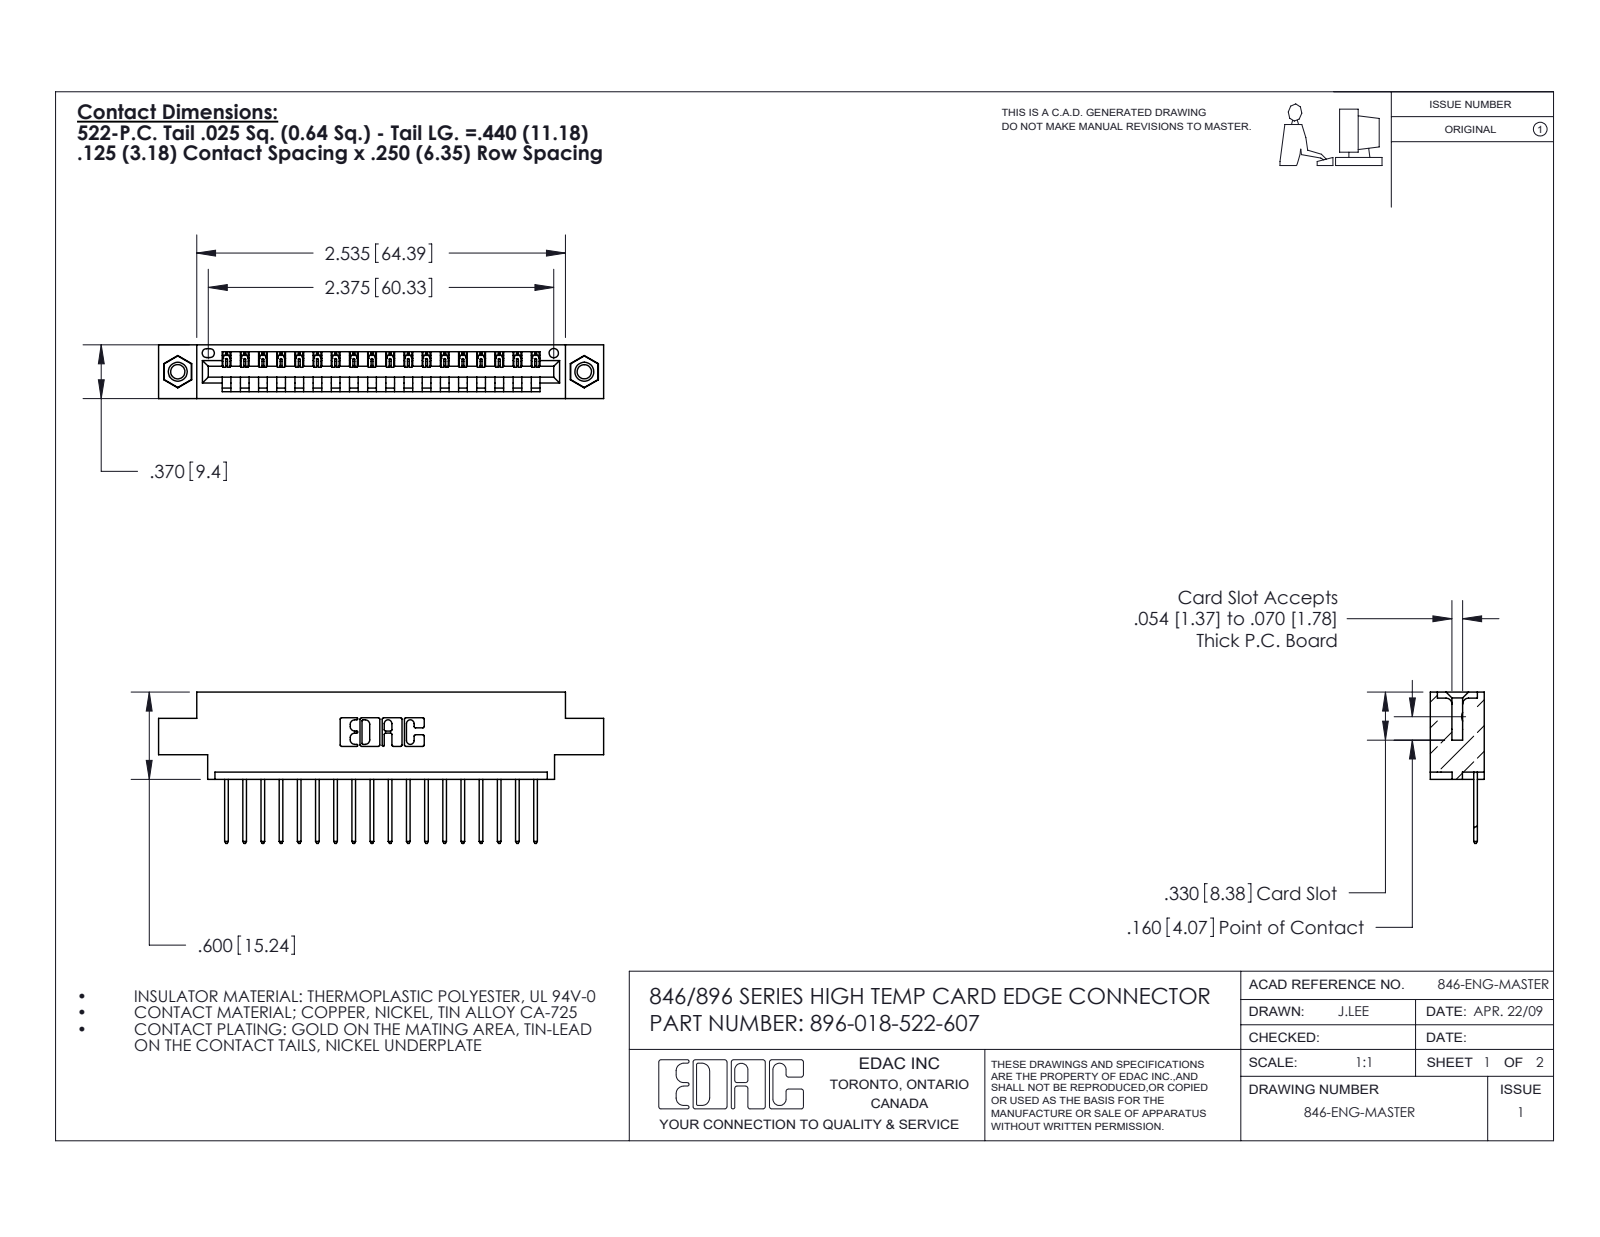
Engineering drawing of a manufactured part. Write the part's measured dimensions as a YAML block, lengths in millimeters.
part_name: "346 Part_0.170 Offset - 0.156 Dia-TI; 396-018-522-607; 345-250-001_345-250-005-103; 345-292-001_345-293-122"
step_written_by: "SolidWorks 2016 (CONFIG_CONTROL_DESIGN)"
units: millimeters
bodies: {solids: 21, faces: 1230, planar: 832, cylindrical: 382, other: 16}
overall_size: [77.7, 26.4, 9.4]
volume: 7110
surface_area: 8890
round_holes:
  - {diameter: 2.5, count: 2}
  - {diameter: 3.2, count: 2}
  - {diameter: 4, count: 2}
  - {diameter: 1.6, count: 1}
round_bosses_or_shafts:
  - {diameter: 3.9, count: 2}
partial_cylinders:
  - {radius: 0.2, count: 36}
  - {radius: 0.3, count: 36}
  - {radius: 0.3, count: 22}
  - {radius: 0.2, count: 6}
  - {radius: 0.8, count: 6}
  - {radius: 0.7, count: 3}
  - {radius: 0.8, count: 2}
  - {radius: 1, count: 2}
face_to_face_distances: [1.2, 8.2, 9.4, 6.4, 1.8, 7.6, 0.6, 5.6, 3.8, 2.5]
hole_center_spacings: [6.2, 65.7, 71]
